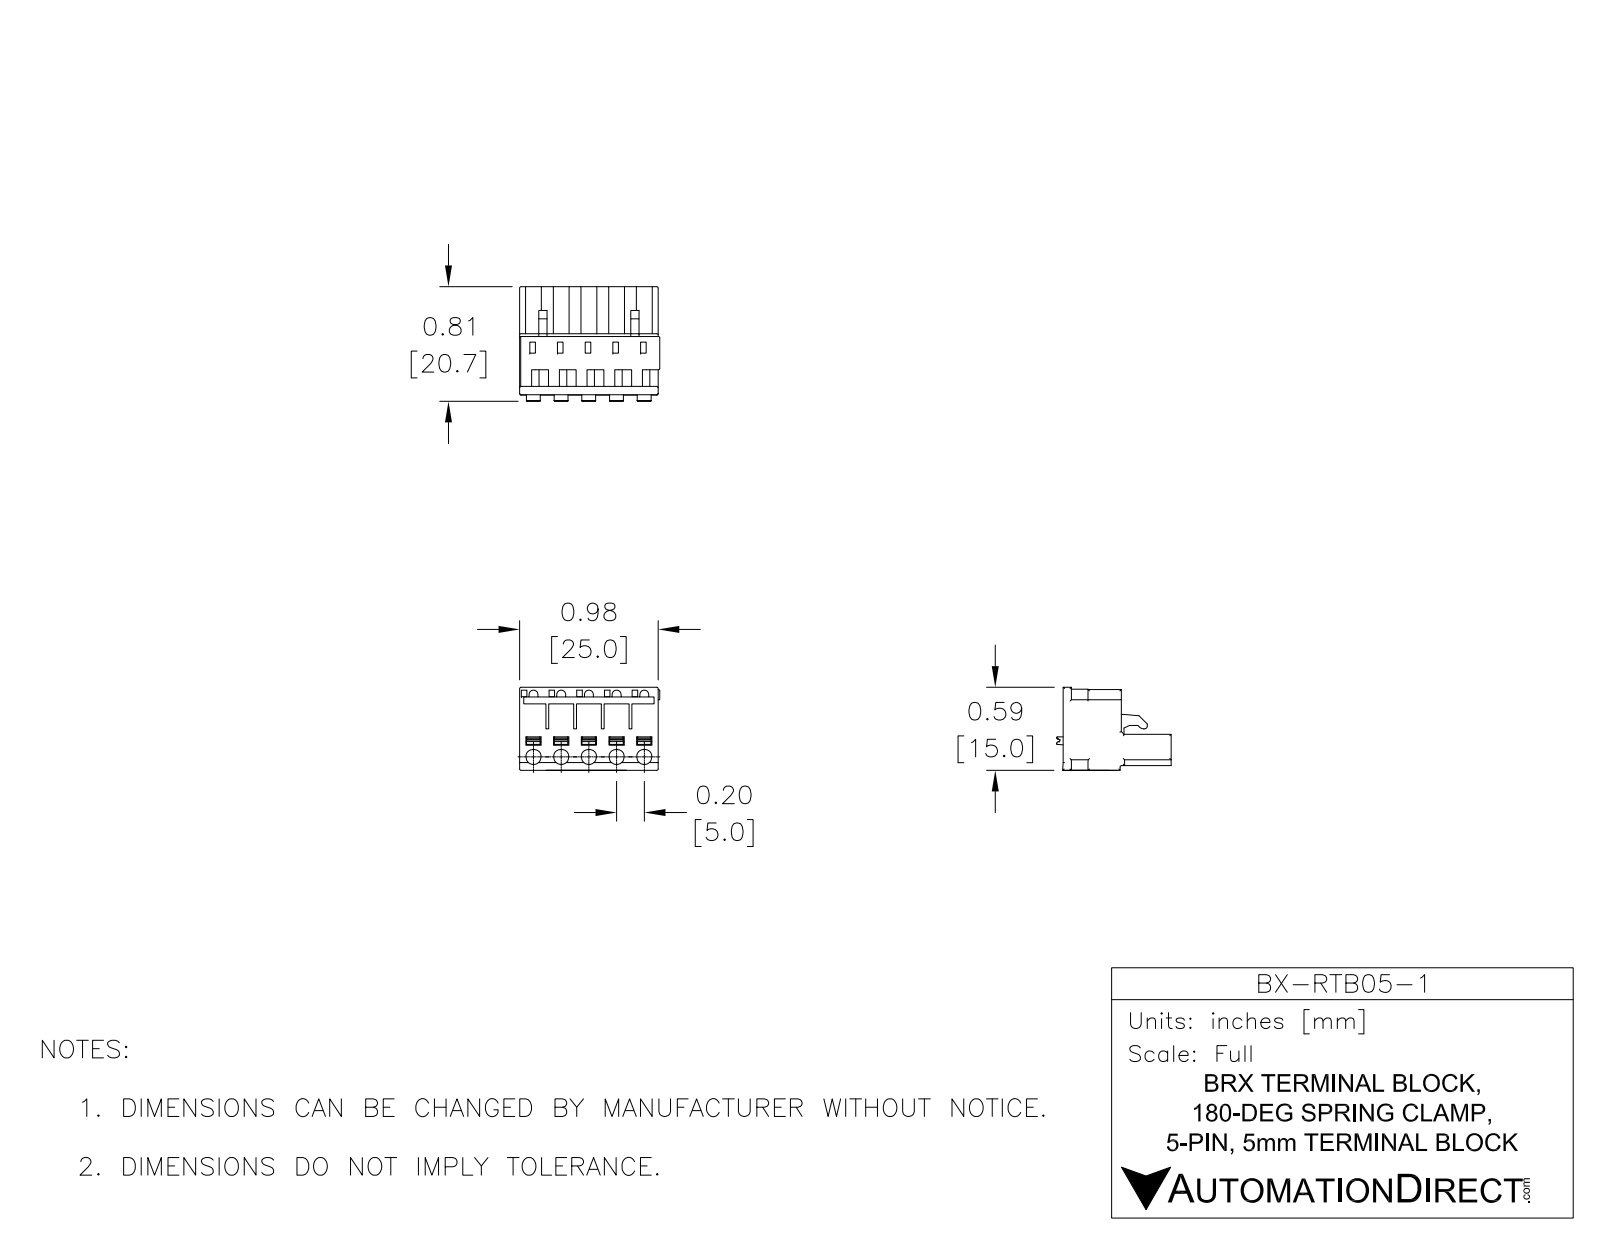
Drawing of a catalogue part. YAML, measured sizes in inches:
part_name: "BX-RTB05-1"
step_written_by: "SolidWorks 2016 (AUTOMOTIVE_DESIGN)"
units: inches
bodies: {solids: 1, faces: 654, planar: 338, cylindrical: 204, other: 112}
overall_size: [0.996, 0.815, 0.591]
volume: 0.273
surface_area: 5.354
round_holes:
  - {diameter: 0.063, count: 5}
  - {diameter: 0.108, count: 5}
  - {diameter: 0.124, count: 5}
partial_cylinders:
  - {radius: 0.004, count: 60}
  - {radius: 0.01, count: 38}
  - {radius: 0.031, count: 5}
  - {radius: 0.039, count: 5}
  - {radius: 0.095, count: 5}
  - {radius: 0.1, count: 5}
  - {radius: 0.008, count: 4}
  - {radius: 0.011, count: 1}
face_to_face_distances: [0.574, 0.984, 0.354, 0.224, 0.35, 0.413, 0.591, 0.059, 0.256, 0.318]
hole_center_spacings: [0.197, 0.2, 0.394, 0.396, 0.591, 0.592, 0.038, 0.037]
